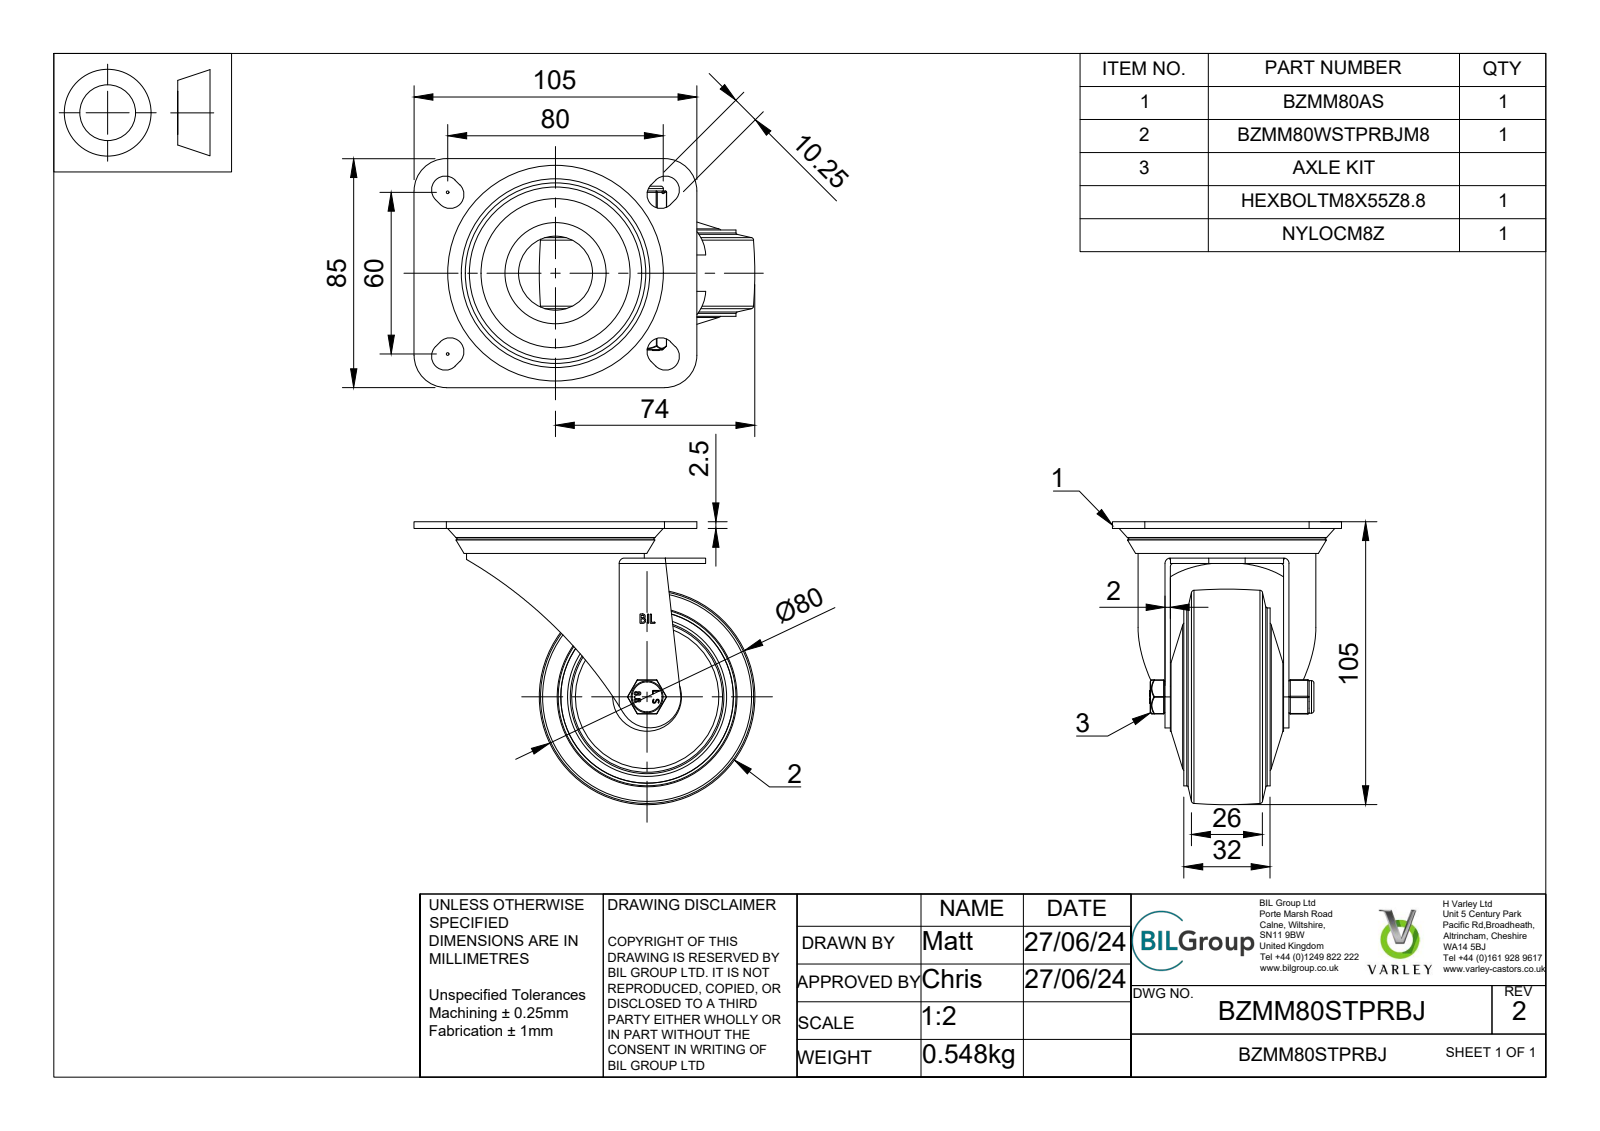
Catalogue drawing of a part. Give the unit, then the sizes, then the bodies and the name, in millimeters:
Units: millimetres
Overall size (bounding box): 126.5 × 105 × 85
Round holes (diameter × count): ⌀0.66 ×2, ⌀8 ×1, ⌀8.2 ×1, ⌀8.5 ×1, ⌀8.6 ×1, ⌀20 ×1, ⌀22.5 ×1, ⌀27.5 ×1, ⌀30 ×1, ⌀31 ×1, ⌀32 ×1, ⌀32.5 ×1
Round bosses / shafts (diameter × count): ⌀66 ×2, ⌀56 ×1, ⌀43 ×1, ⌀39 ×1, ⌀34.5 ×1, ⌀31.5 ×1, ⌀30.5 ×1, ⌀25.5 ×1
Partial cylindrical surfaces — rounded edges, fillets, slot ends (radius × count): R0.5 ×18, R0.25 ×12, R5.12 ×8, R12 ×5, R0.33 ×4, R0.64 ×4, R1 ×4, R0.63 ×2
Main face-to-face distances: 2, 2.5, 5, 10.5, 11, 21, 0.5, 7, 23, 15.5
Hole centre spacings: 3.22, 2.49
Volume: 159 764 mm³ · Surface area: 118 629 mm²
Bodies: 47 solids, 774 faces (269 planar, 199 cylindrical, 306 other)
Part name (STEP PRODUCT): BZMM80STPRBJ v3; BZMM80WSTPRBJM8 v1; 65 SHORE A THERMOPLASTIC RUBBER TYRE; POLYPROPYLENE RIM (+8 more)
STEP written by: Autodesk Translation Framework v13.14.0.145 (AUTOMOTIVE_DESIGN)
